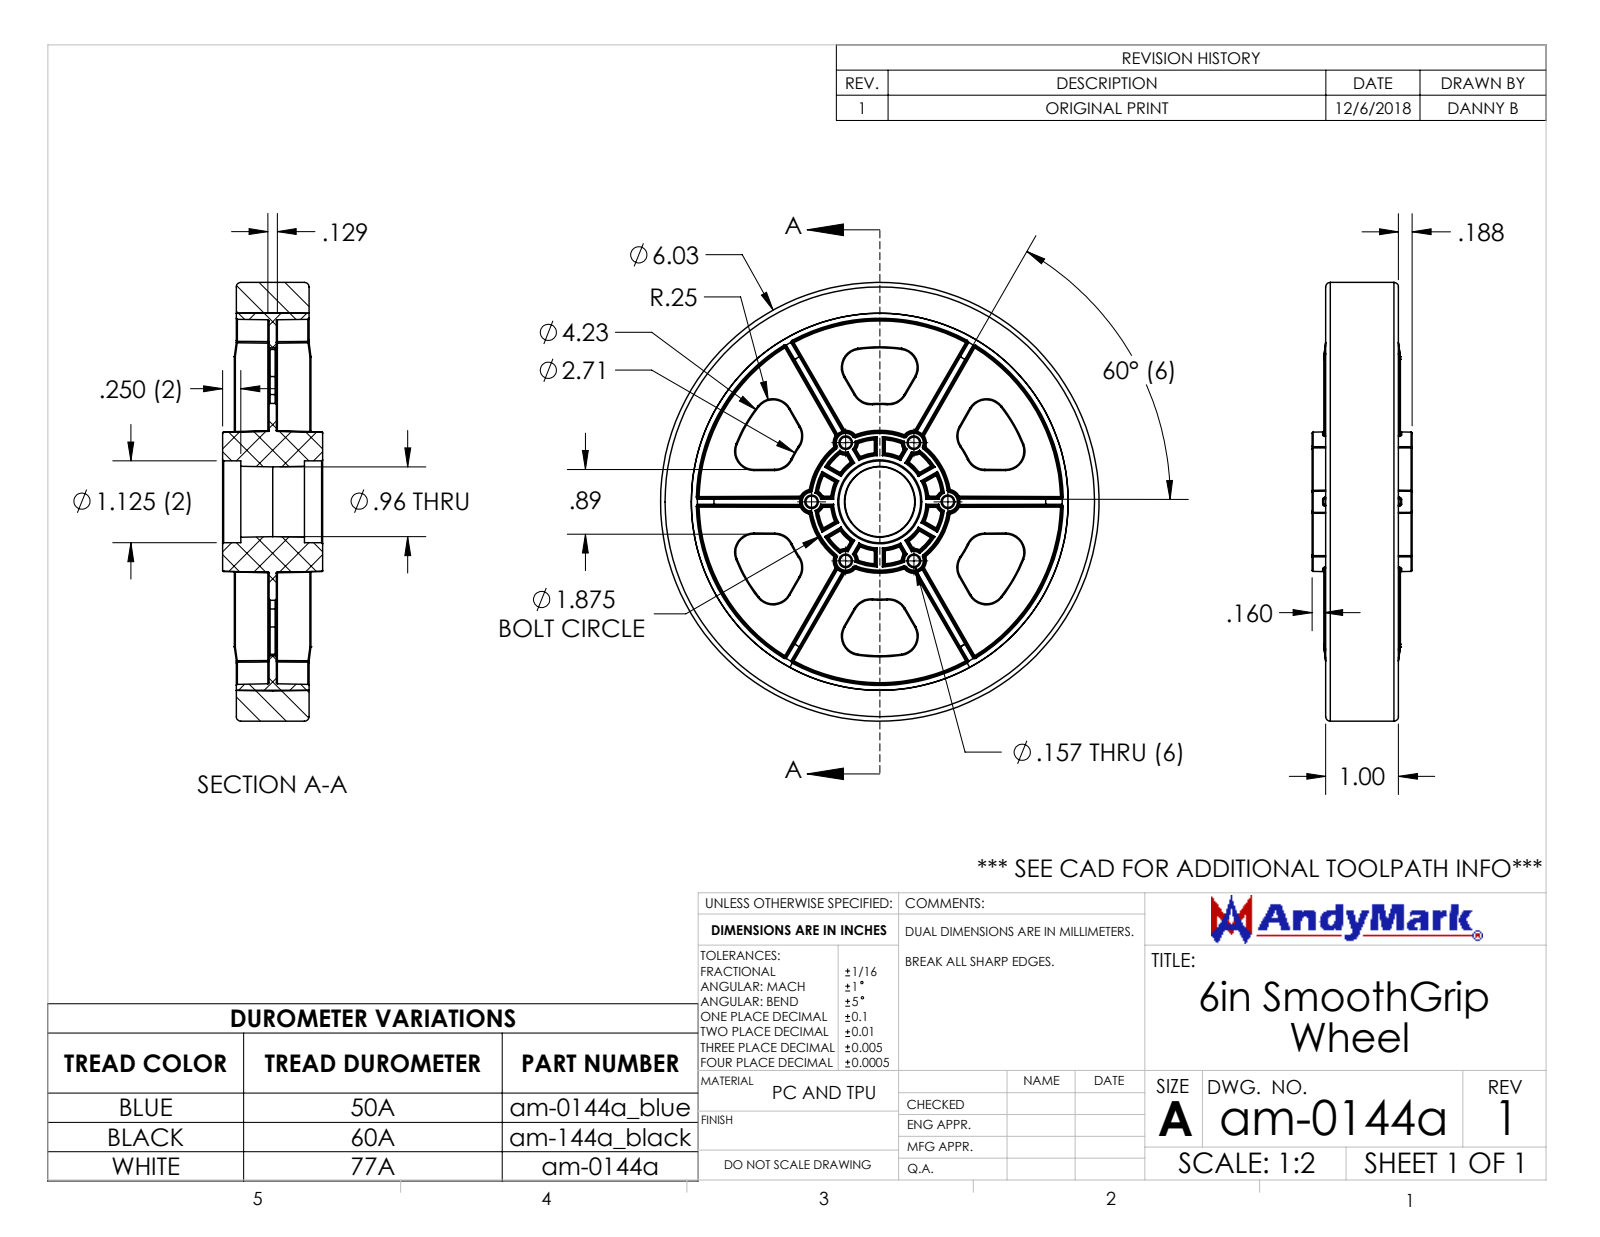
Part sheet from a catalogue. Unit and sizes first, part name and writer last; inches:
Units: inches
Overall size (bounding box): 6.03 × 6.03 × 1.375
Round holes (diameter × count): ⌀0.157 ×6, ⌀1.125 ×1, ⌀5.182 ×1
Round bosses / shafts (diameter × count): ⌀6.03 ×1
Partial cylindrical surfaces — rounded edges, fillets, slot ends (radius × count): R0.015 ×151, R0.25 ×24, R1.353 ×1, R2.116 ×1
Main face-to-face distances: 0.45, 0.55, 0.1, 0.128, 1, 0.124, 0.187, 0.637, 0.737, 1.187
Hole centre spacings: 0.937, 1.624, 1.875, 0.938
Volume: 13.09 in³ · Surface area: 158.4 in²
Bodies: 2 solids, 1583 faces (153 planar, 269 cylindrical, 1161 other)
Part name (STEP PRODUCT): am-0144a SmoothGrip Wheel; SmoothGrip Tread; 6 wheel Rev 4
STEP written by: SolidWorks 2018 (AUTOMOTIVE_DESIGN)
